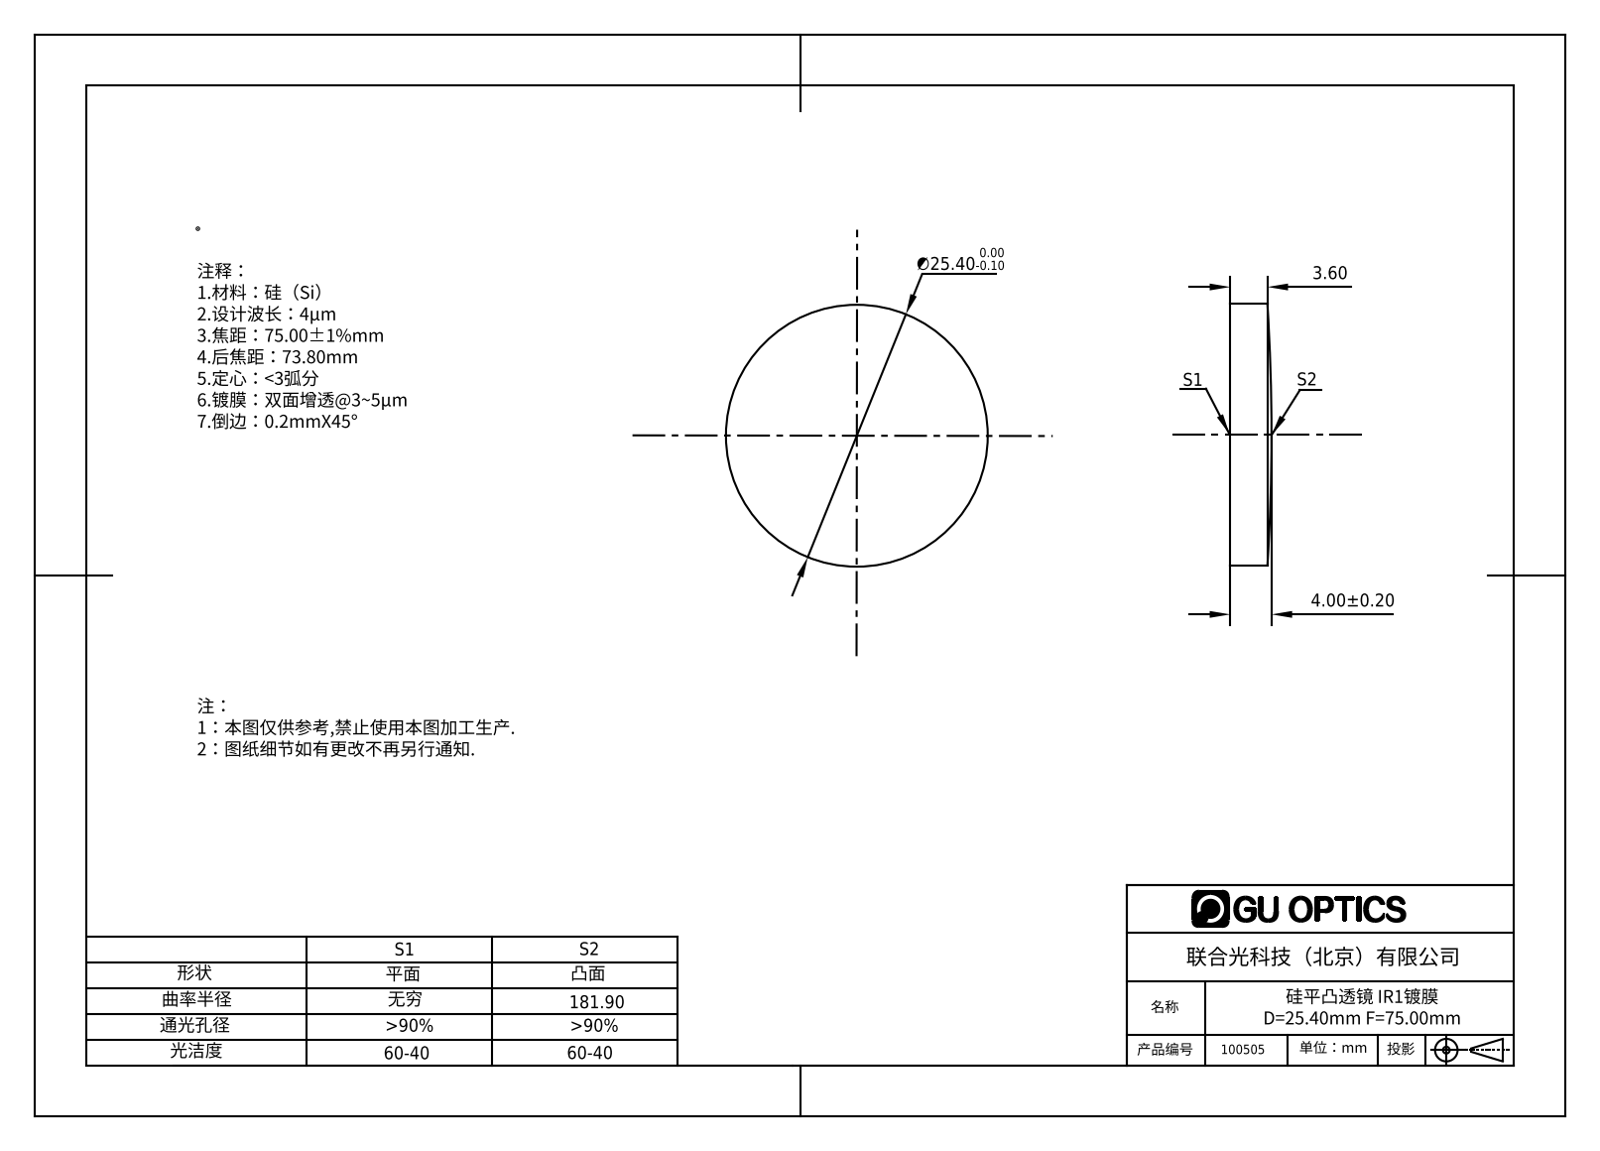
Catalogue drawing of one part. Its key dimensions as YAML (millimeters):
part_name: "100493"
step_written_by: "SolidWorks 2016 (AUTOMOTIVE_DESIGN)"
units: millimeters
bodies: {solids: 1, faces: 5, planar: 1, cylindrical: 2, other: 2}
overall_size: [25.4, 25.4, 4]
volume: 1926
surface_area: 1301
round_bosses_or_shafts:
  - {diameter: 25.4, count: 1}
